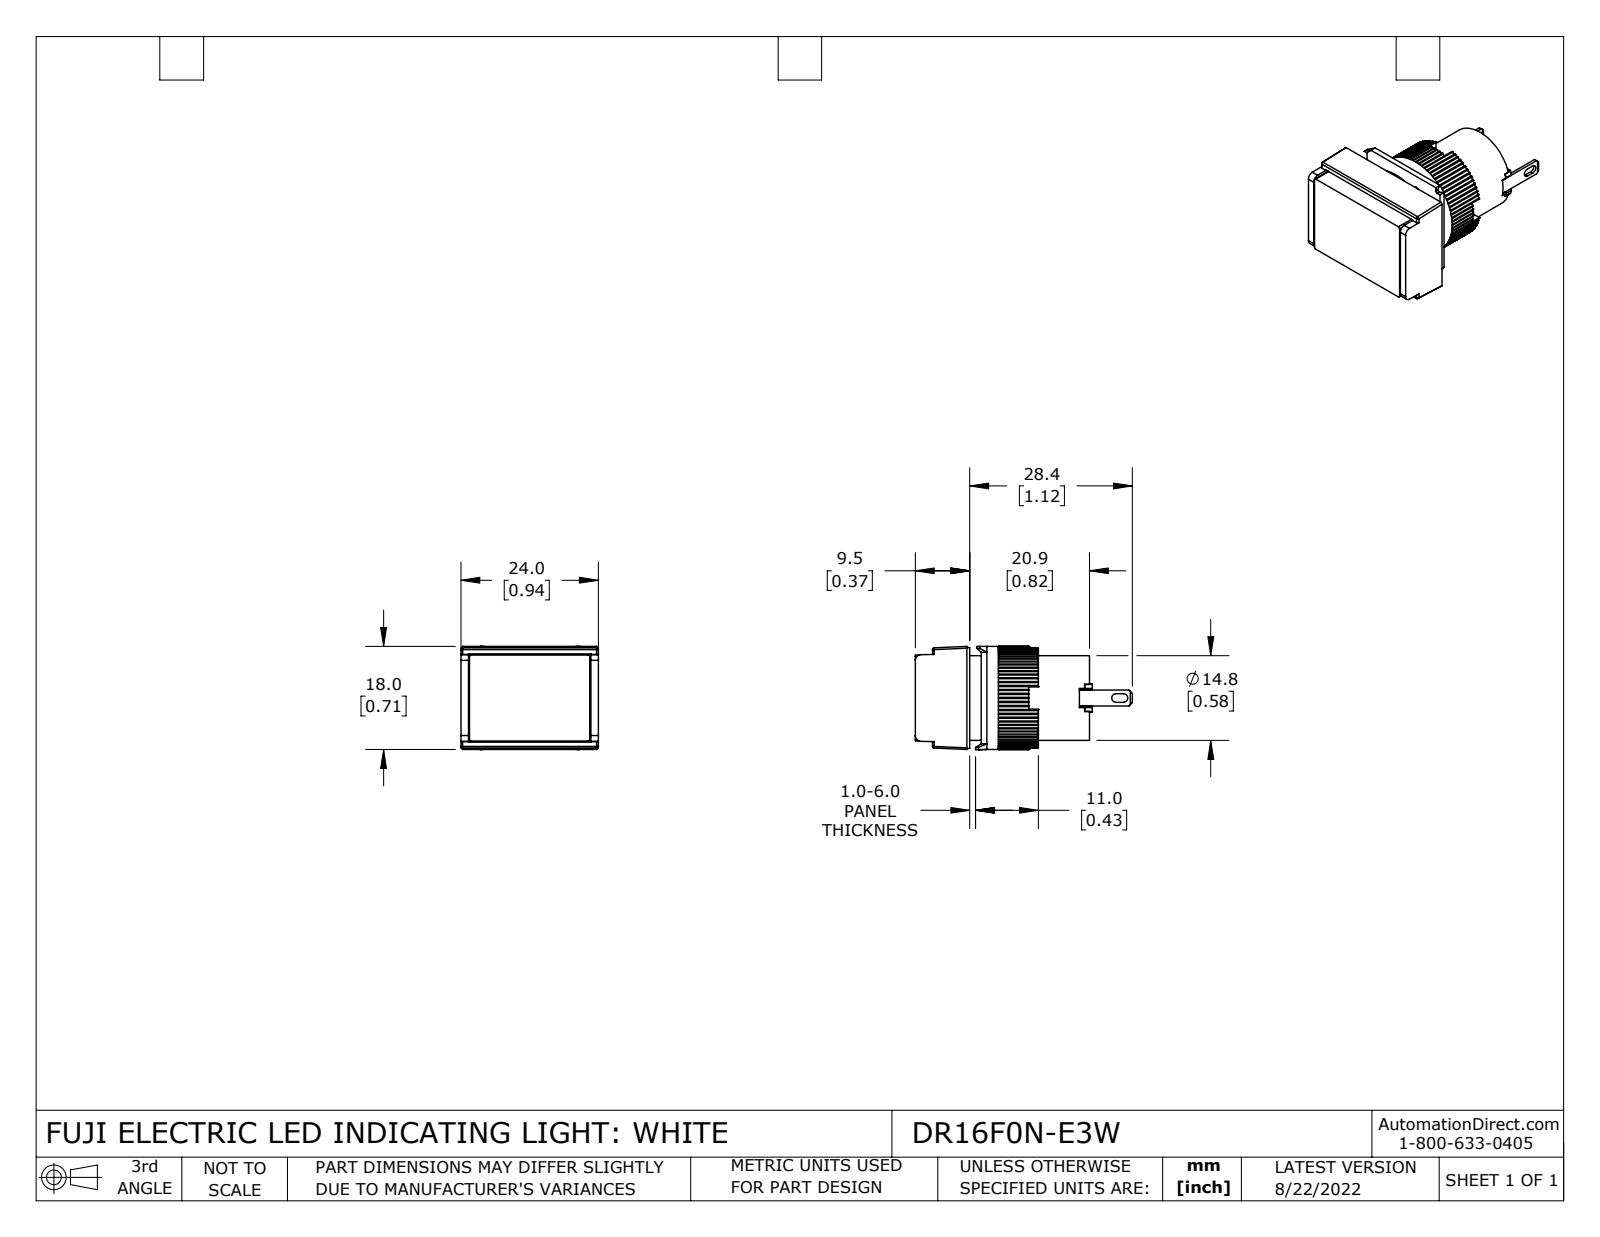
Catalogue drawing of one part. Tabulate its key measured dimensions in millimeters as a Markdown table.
| quantity | value |
| --- | --- |
| part name | DR16F0N-E3W |
| STEP written by | SolidWorks 2021 (CONFIG_CONTROL_DESIGN) |
| units | millimeters |
| bodies | 10 solids, 501 faces (322 planar, 175 cylindrical, 4 other) |
| overall size | 37.9 × 24 × 18 |
| volume | 7 340 mm³ |
| surface area | 5 777 mm² |
| round holes (diameter × count) | 13.8 × 1, 14.8 × 1 |
| round bosses / shafts (diameter × count) | 18 × 1, 17.6 × 1 |
| partial cylindrical surfaces (radius × count) | 0.3 × 80, 0.2 × 8, 0.3 × 6, 0.8 × 2, 1 × 2 |
| main face-to-face distances | 5.4, 9, 3.6, 8.9, 12.5, 3.5, 21.4, 17.9, 11.5, 1.5 |
